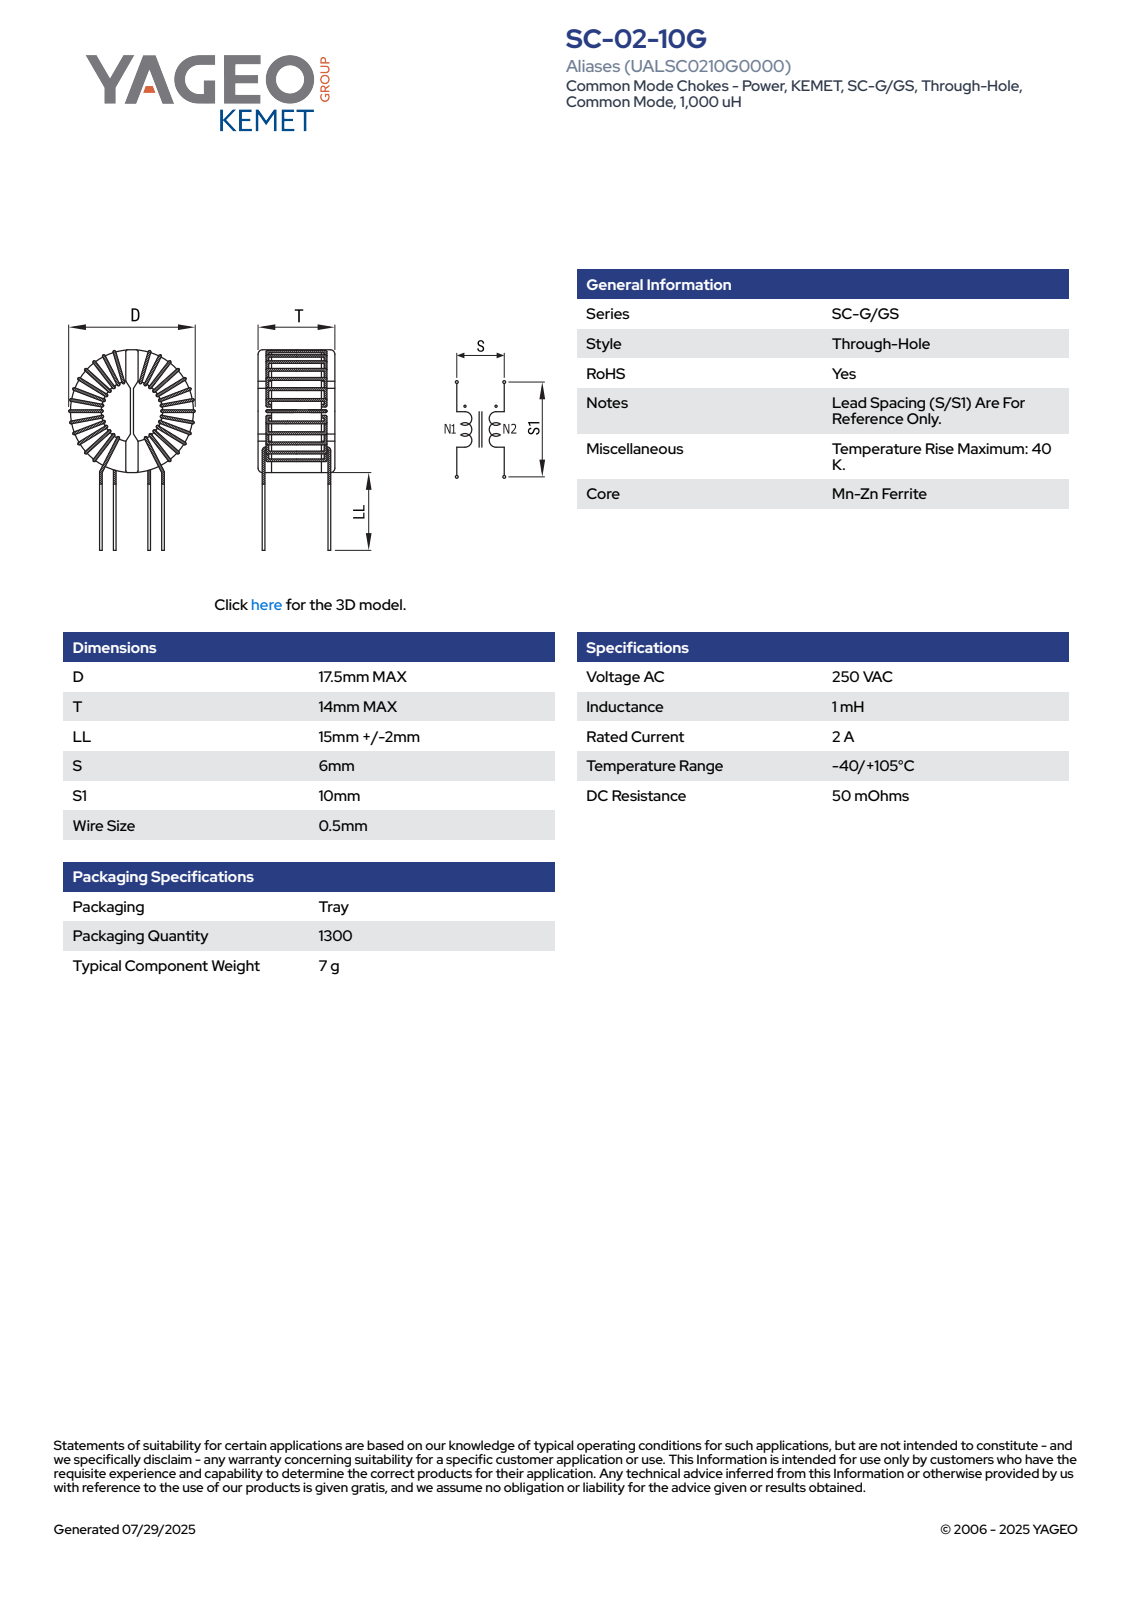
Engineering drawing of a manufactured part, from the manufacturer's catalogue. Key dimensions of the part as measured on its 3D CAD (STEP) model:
Part name (STEP PRODUCT): SC-02-10G
STEP written by: SolidWorks 2018 (AUTOMOTIVE_DESIGN)
Units: millimetres
Bodies: 1 solid, 268 faces (121 planar, 65 cylindrical, 82 other)
Overall size (bounding box): 30.36 × 17.5 × 14
Volume: 1 791 mm³ · Surface area: 1 733 mm²
Round bosses / shafts (diameter × count): ⌀0.5 ×8
Partial cylindrical surfaces — rounded edges, fillets, slot ends (radius × count): R0.25 ×16, R2.32 ×1, R3.21 ×1, R3.62 ×1, R3.67 ×1, R3.8 ×1, R6.35 ×1, R6.4 ×1
Main face-to-face distances: 1.2, 2, 8.3, 0.8, 3.2, 2.85, 11.15, 1.15, 2.05, 0.85
